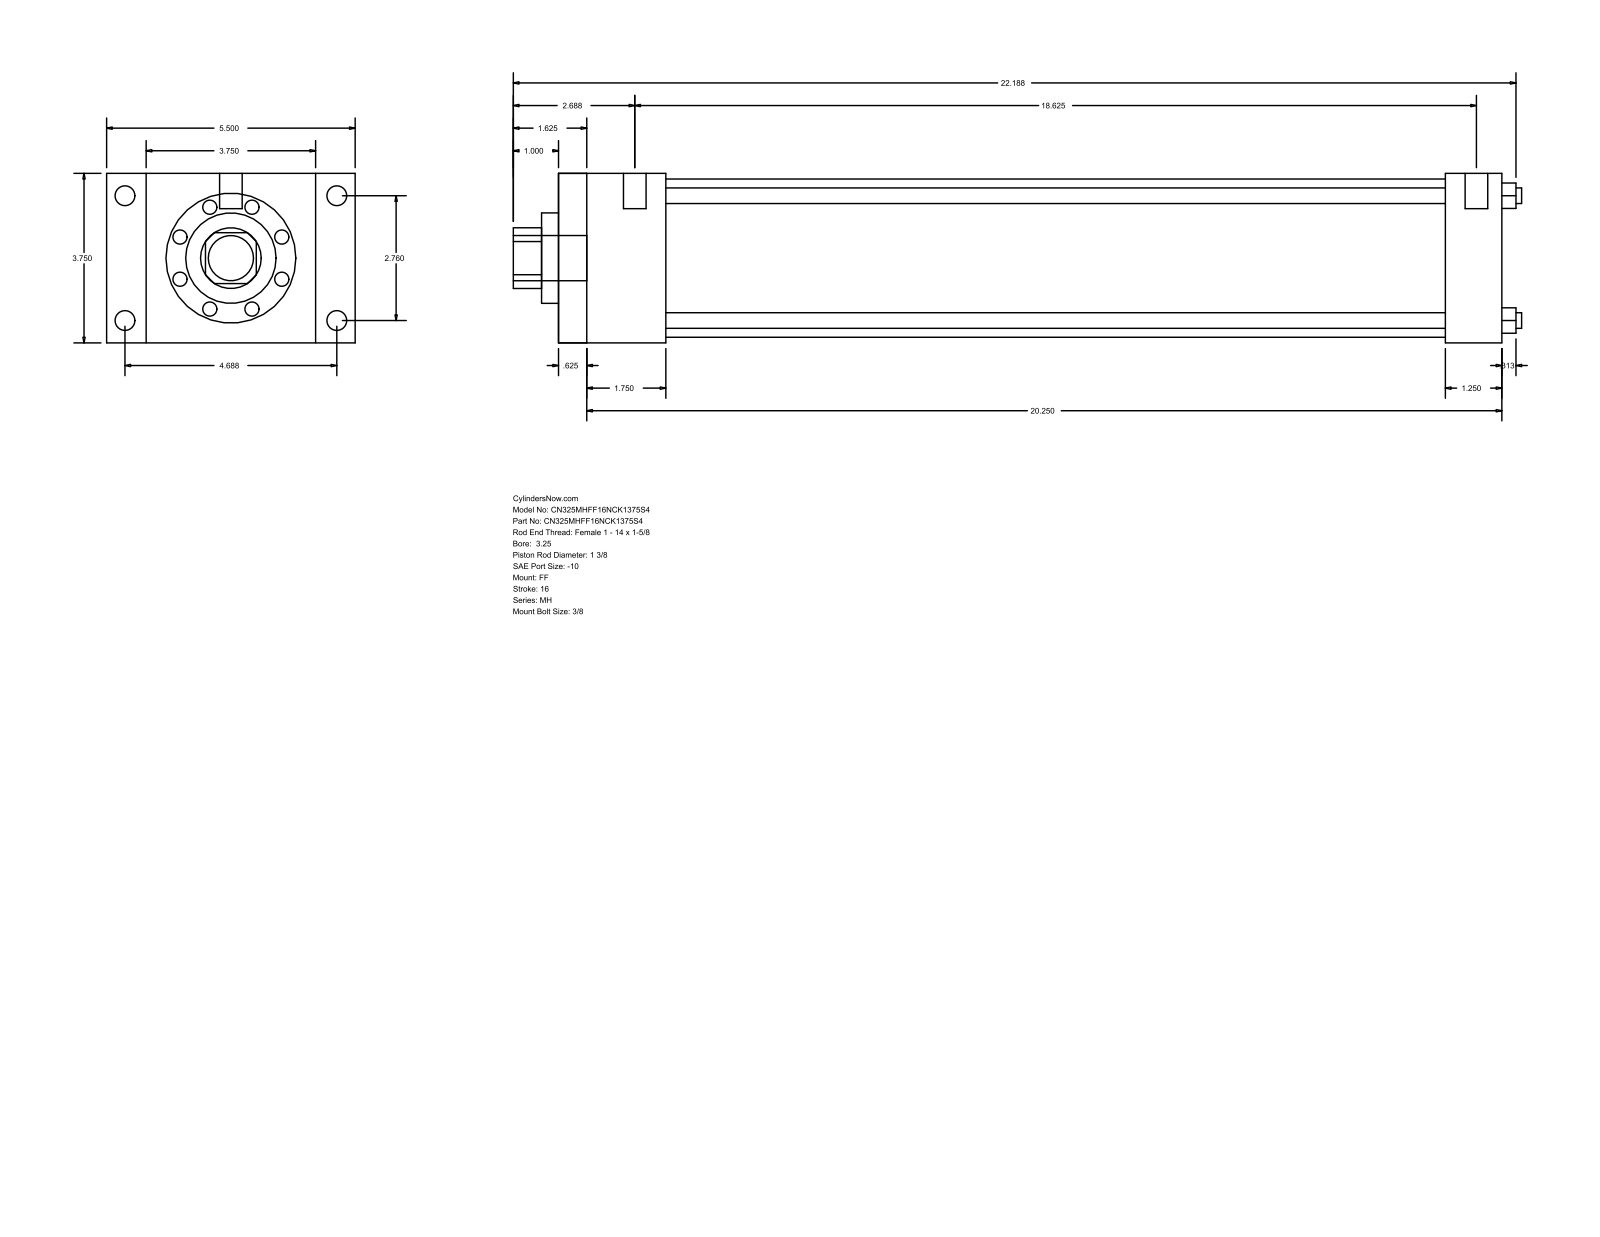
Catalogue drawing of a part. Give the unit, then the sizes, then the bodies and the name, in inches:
Units: inches
Overall size (bounding box): 22.313 × 5.5 × 3.75
Round holes (diameter × count): ⌀0.345 ×4, ⌀1.375 ×1, ⌀2 ×1, ⌀3.5 ×1
Round bosses / shafts (diameter × count): ⌀0.438 ×4, ⌀0.219 ×4, ⌀0.5 ×2, ⌀1 ×1
Partial cylindrical surfaces — rounded edges, fillets, slot ends (radius × count): R0.672 ×1
Main face-to-face distances: 3.75, 20.875, 0.625, 20.25, 0.875, 4.625, 19.625, 19, 1.25, 2.375
Hole centre spacings: 1.952, 2.76, 3.903
Bodies: 0 solids, 92 faces (64 planar, 28 cylindrical, 0 other)
Part name (STEP PRODUCT): MH_FF__0325_1.375
STEP written by: GSSL Pune (CONFIG_CONTROL_DESIGN)
